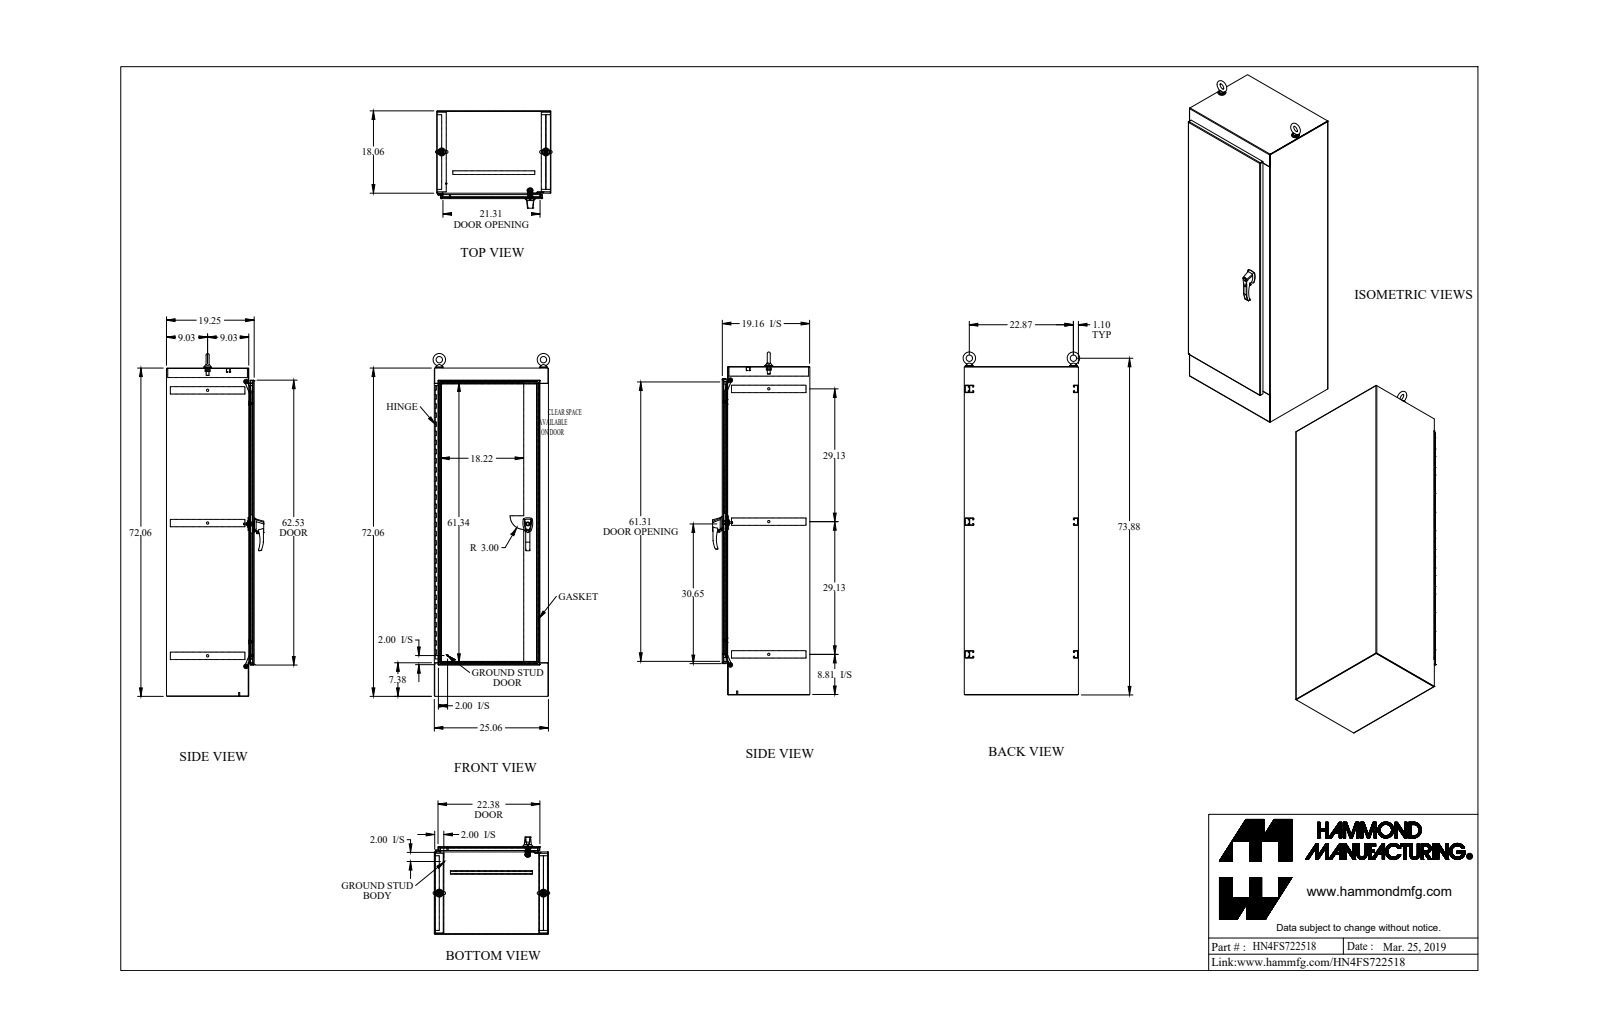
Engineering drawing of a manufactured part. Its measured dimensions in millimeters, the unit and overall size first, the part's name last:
Units: millimetres
Overall size (bounding box): 1911.4 × 650.3 × 542.6
Round holes (diameter × count): ⌀7.7 ×10, ⌀8.9 ×7, ⌀12.7 ×3, ⌀6.4 ×2, ⌀6.5 ×2, ⌀7.1 ×2, ⌀7.1 ×2, ⌀8 ×2, ⌀9.9 ×2, ⌀10.5 ×2, ⌀13.4 ×2, ⌀15.9 ×2
Round bosses / shafts (diameter × count): ⌀7.1 ×4, ⌀44.5 ×2, ⌀38.1 ×2, ⌀31.8 ×2, ⌀25.4 ×2, ⌀19.1 ×2, ⌀18.7 ×2, ⌀16 ×2
Partial cylindrical surfaces — rounded edges, fillets, slot ends (radius × count): R1.1 ×60, R3.5 ×54, R12.7 ×23, R3.2 ×22, R0.5 ×16, R1.2 ×15, R1.5 ×15, R3.6 ×15
Main face-to-face distances: 2.4, 486.5, 634.1, 631.7, 484, 488.9, 636.5, 456.3, 30.1, 1827.9
Hole centre spacings: 152.4, 304.8, 457.2, 609.6, 762, 914.4, 1066.8, 0.4
Volume: 14 090 000 mm³ · Surface area: 11 630 000 mm²
Bodies: 55 solids, 1954 faces (906 planar, 883 cylindrical, 165 other)
Part name (STEP PRODUCT): HN4FS722518
STEP written by: SolidWorks 2018 (AUTOMOTIVE_DESIGN)
